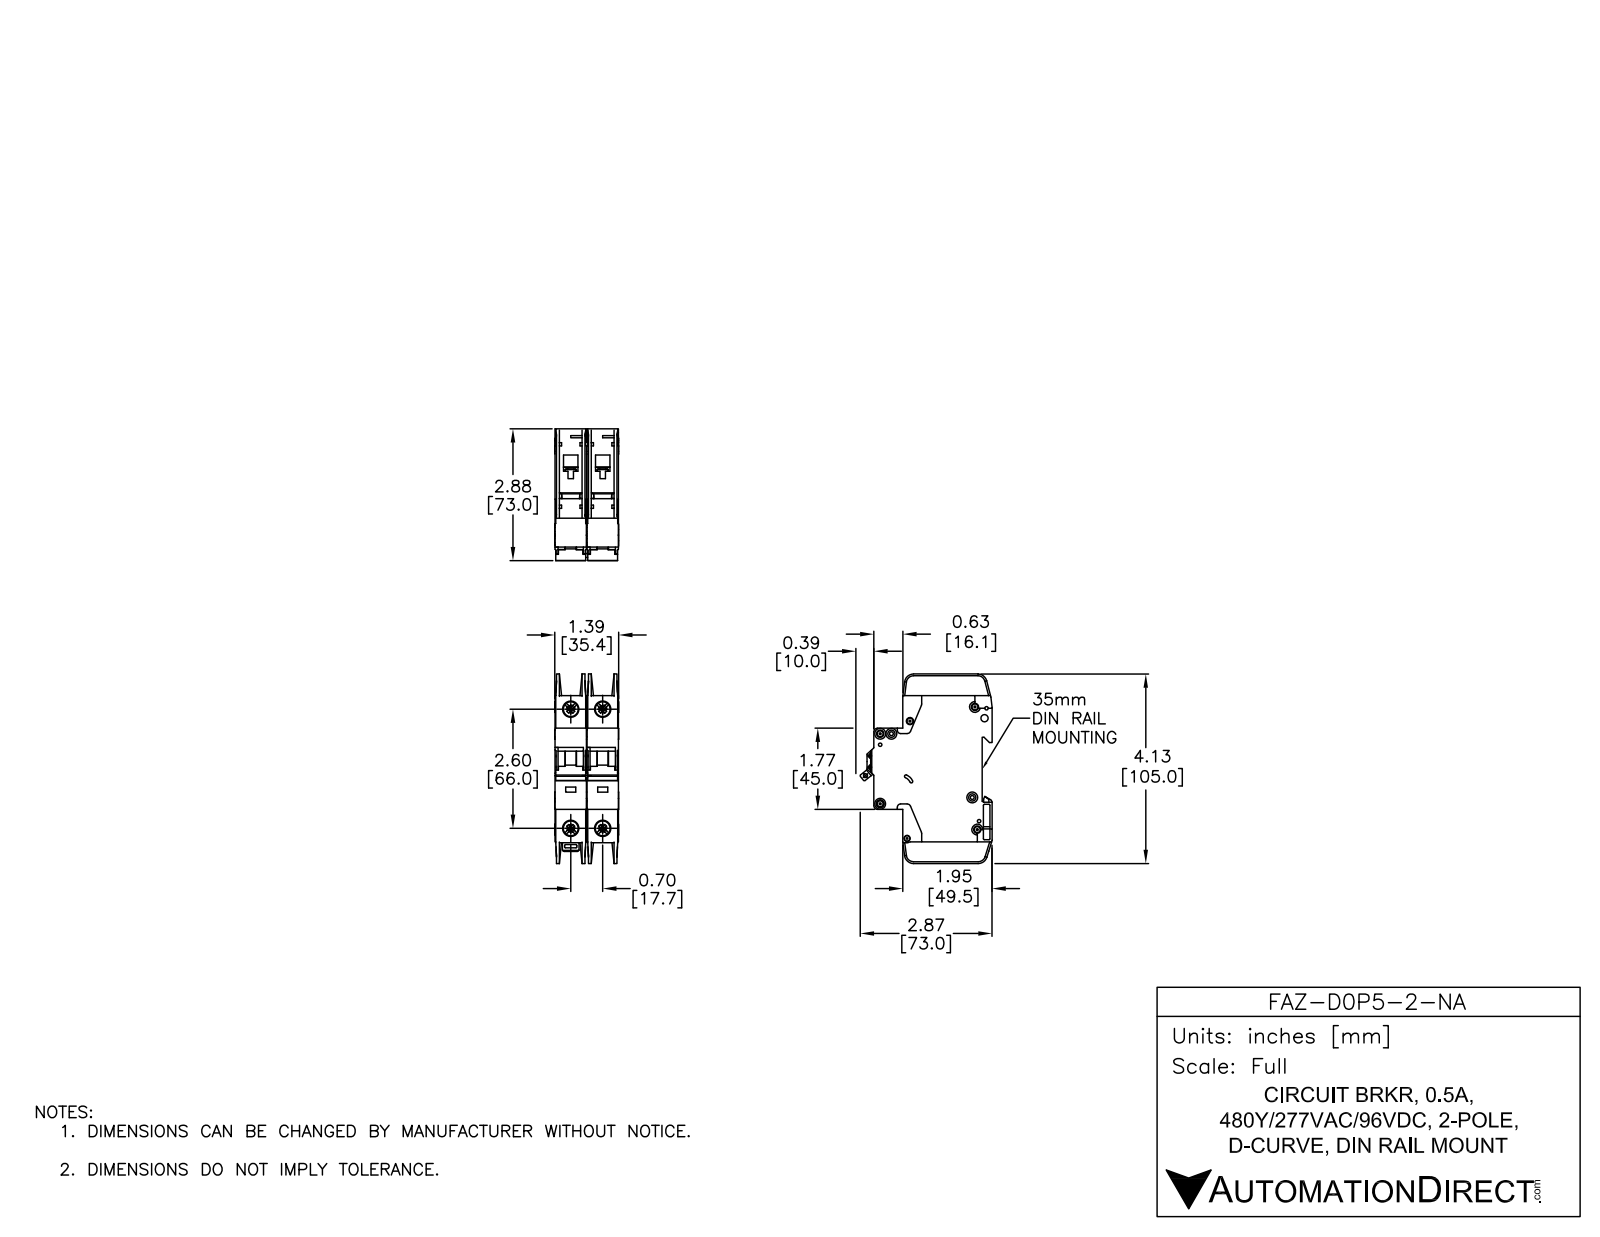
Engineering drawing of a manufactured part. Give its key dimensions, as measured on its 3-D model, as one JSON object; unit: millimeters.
{"part_name": "FAZ-D0P5-2-NA", "step_written_by": "SolidWorks 2014 (AUTOMOTIVE_DESIGN)", "units": "millimeters", "bodies": {"solids": 6, "faces": 1568, "planar": 818, "cylindrical": 526, "other": 224}, "overall_size": [105, 73.04, 35.4], "volume_mm3": 155390, "surface_area_mm2": 49479, "round_holes": [[3.6, 7], [7.15, 4], [8.2, 4], [1.09, 2], [1.5, 2], [4, 2], [1.9, 1], [2.15, 1], [2.2, 1], [2.55, 1], [3.3, 1], [3.4, 1]], "round_bosses_or_shafts": [[6, 7], [2.5, 2]], "partial_cylinders_radius": [[0.25, 47], [0.5, 24], [1, 18], [2, 12], [5, 5], [1.8, 4], [4, 4], [0.2, 2]], "face_to_face_distances": [17.7, 17.5, 0.7, 15.05, 2.45, 1.75, 15.75, 13.3, 35.2, 17], "hole_center_spacings": [6.2, 17.7, 66, 68.33, 5.19, 6.1, 8.19, 8.56]}
